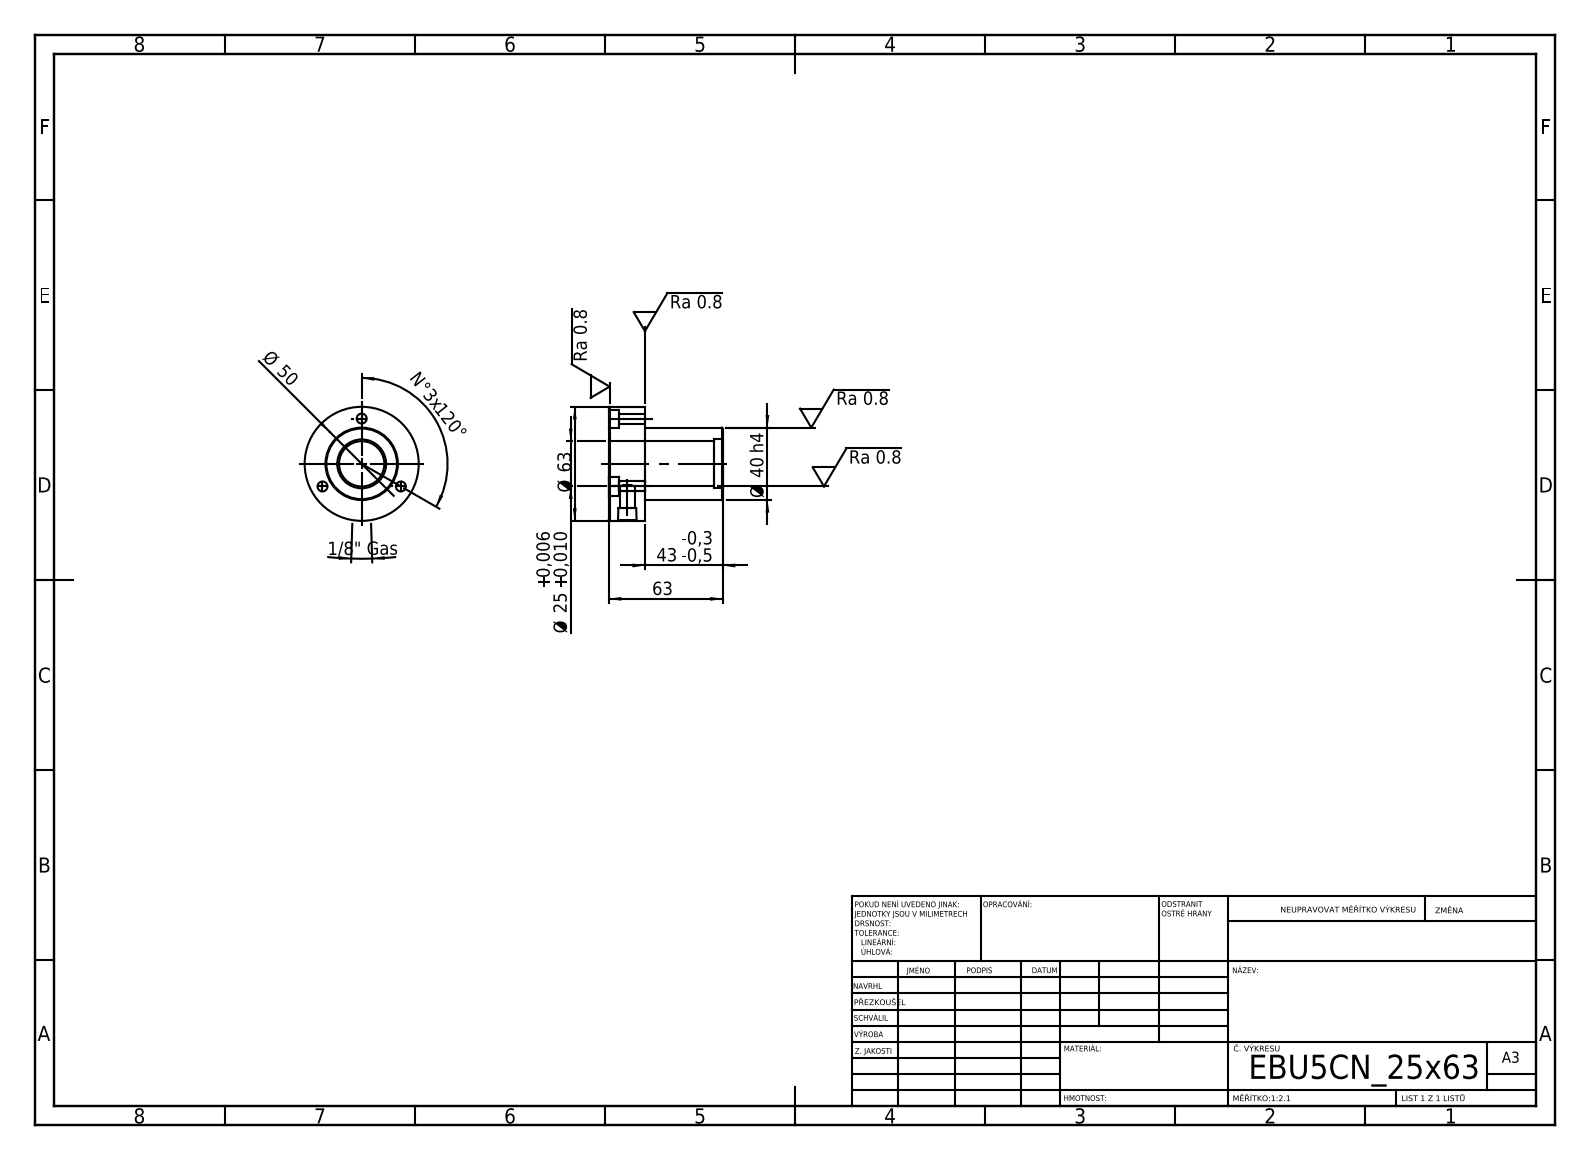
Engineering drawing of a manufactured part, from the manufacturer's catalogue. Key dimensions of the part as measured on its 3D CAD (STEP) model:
STEP written by: SolidWorks 2019 (CONFIG_CONTROL_DESIGN)
Units: millimetres
Bodies: 1 solid, 36 faces (8 planar, 22 cylindrical, 6 other)
Overall size (bounding box): 63 × 63 × 63
Volume: 81 465 mm³ · Surface area: 21 045 mm²
Round holes (diameter × count): ⌀5.5 ×3, ⌀10 ×3, ⌀8.43 ×1, ⌀25 ×1, ⌀27 ×1
Round bosses / shafts (diameter × count): ⌀63 ×1, ⌀40 ×1
Main face-to-face distances: 20, 43, 63, 57.6, 14.6, 5.4, 5, 38, 52.6, 58
Hole centre spacings: 25, 43.3
